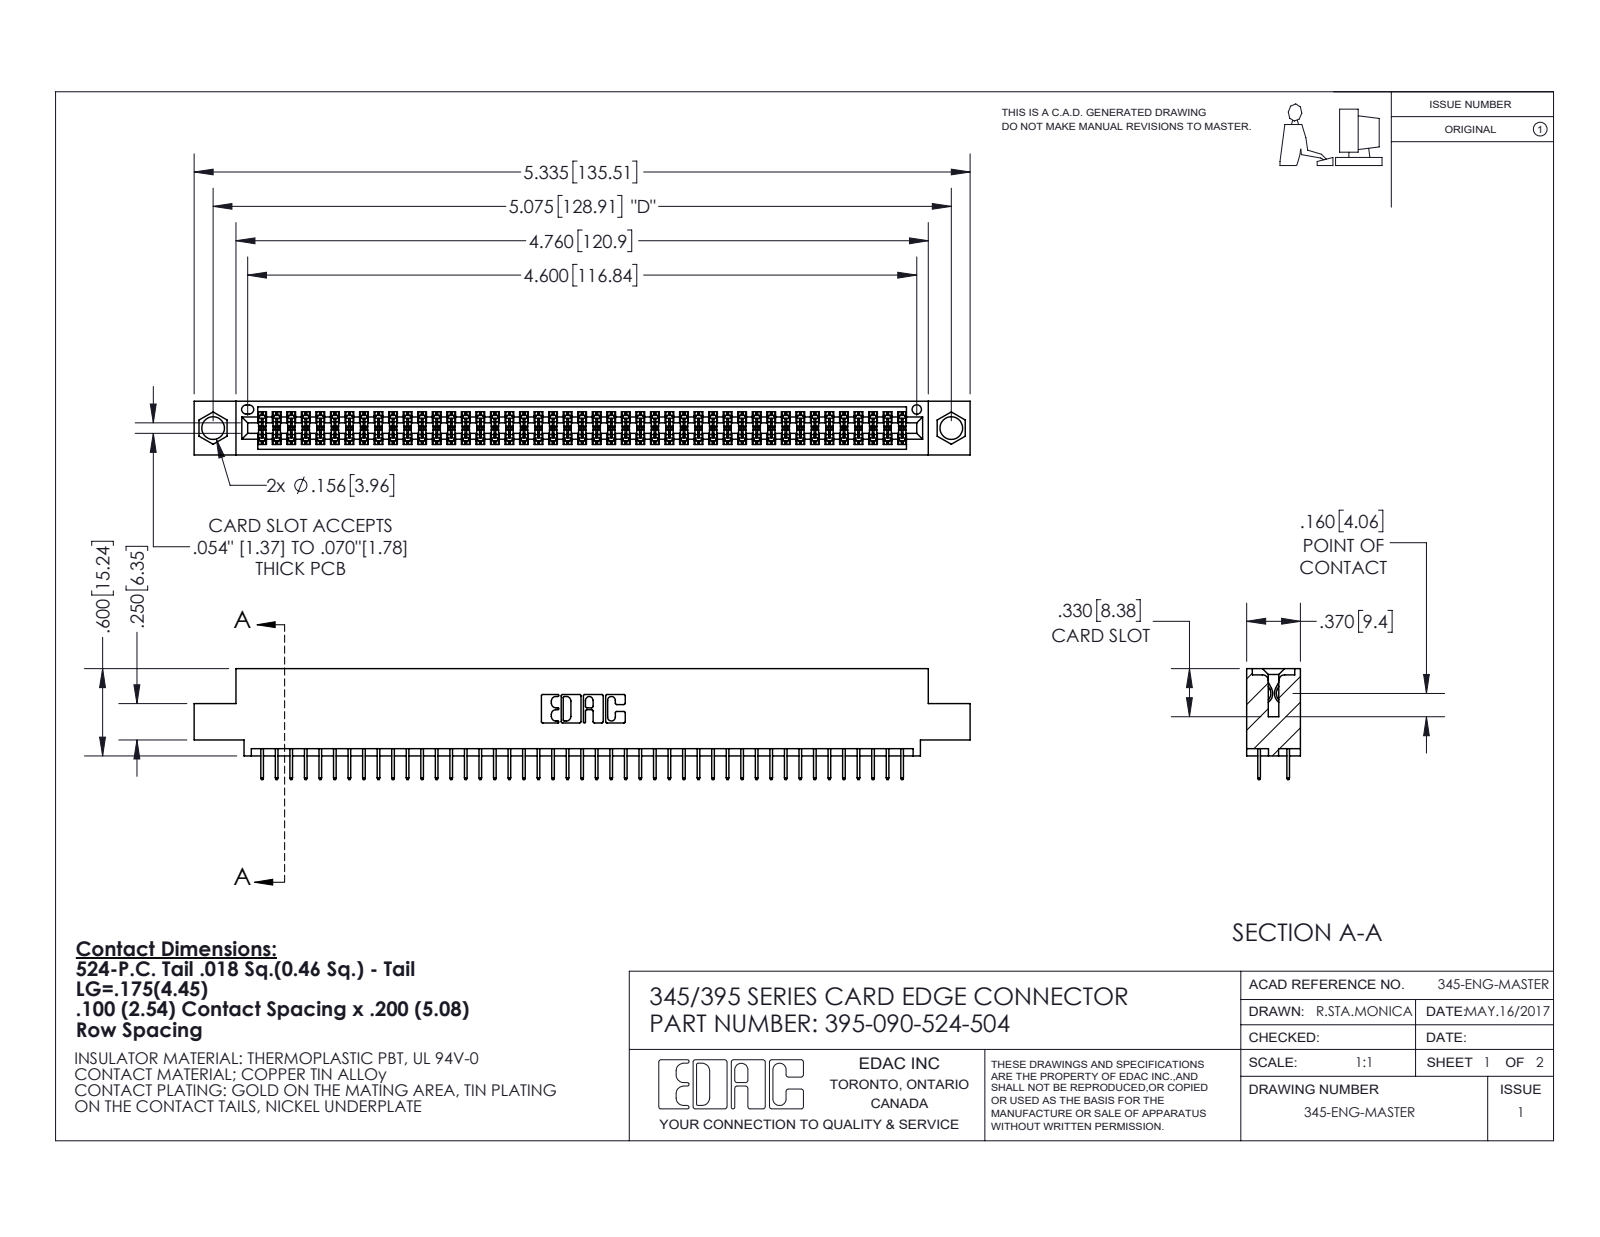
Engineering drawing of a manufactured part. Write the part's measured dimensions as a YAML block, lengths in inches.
part_name: "345 Part_0.110 Offset - 0.156 Dia-TI; 345-292-001_345-293-124; 395-090-524-504"
step_written_by: "SolidWorks 2020 (CONFIG_CONTROL_DESIGN)"
units: inches
bodies: {solids: 91, faces: 5004, planar: 3608, cylindrical: 1396, other: 0}
overall_size: [5.335, 0.762, 0.37]
volume: 0.786
surface_area: 28.95
round_holes:
  - {diameter: 0.156, count: 2}
  - {diameter: 0.064, count: 1}
partial_cylinders:
  - {radius: 0.006, count: 135}
  - {radius: 0.01, count: 22}
  - {radius: 0.007, count: 6}
  - {radius: 0.031, count: 6}
  - {radius: 0.026, count: 3}
  - {radius: 0.014, count: 2}
  - {radius: 0.019, count: 2}
  - {radius: 0.022, count: 2}
face_to_face_distances: [0.072, 0.298, 0.2, 0.37, 0.098, 0.272, 0.025, 0.225, 0.072, 0.175]
hole_center_spacings: [0.27, 4.839, 5.075]
